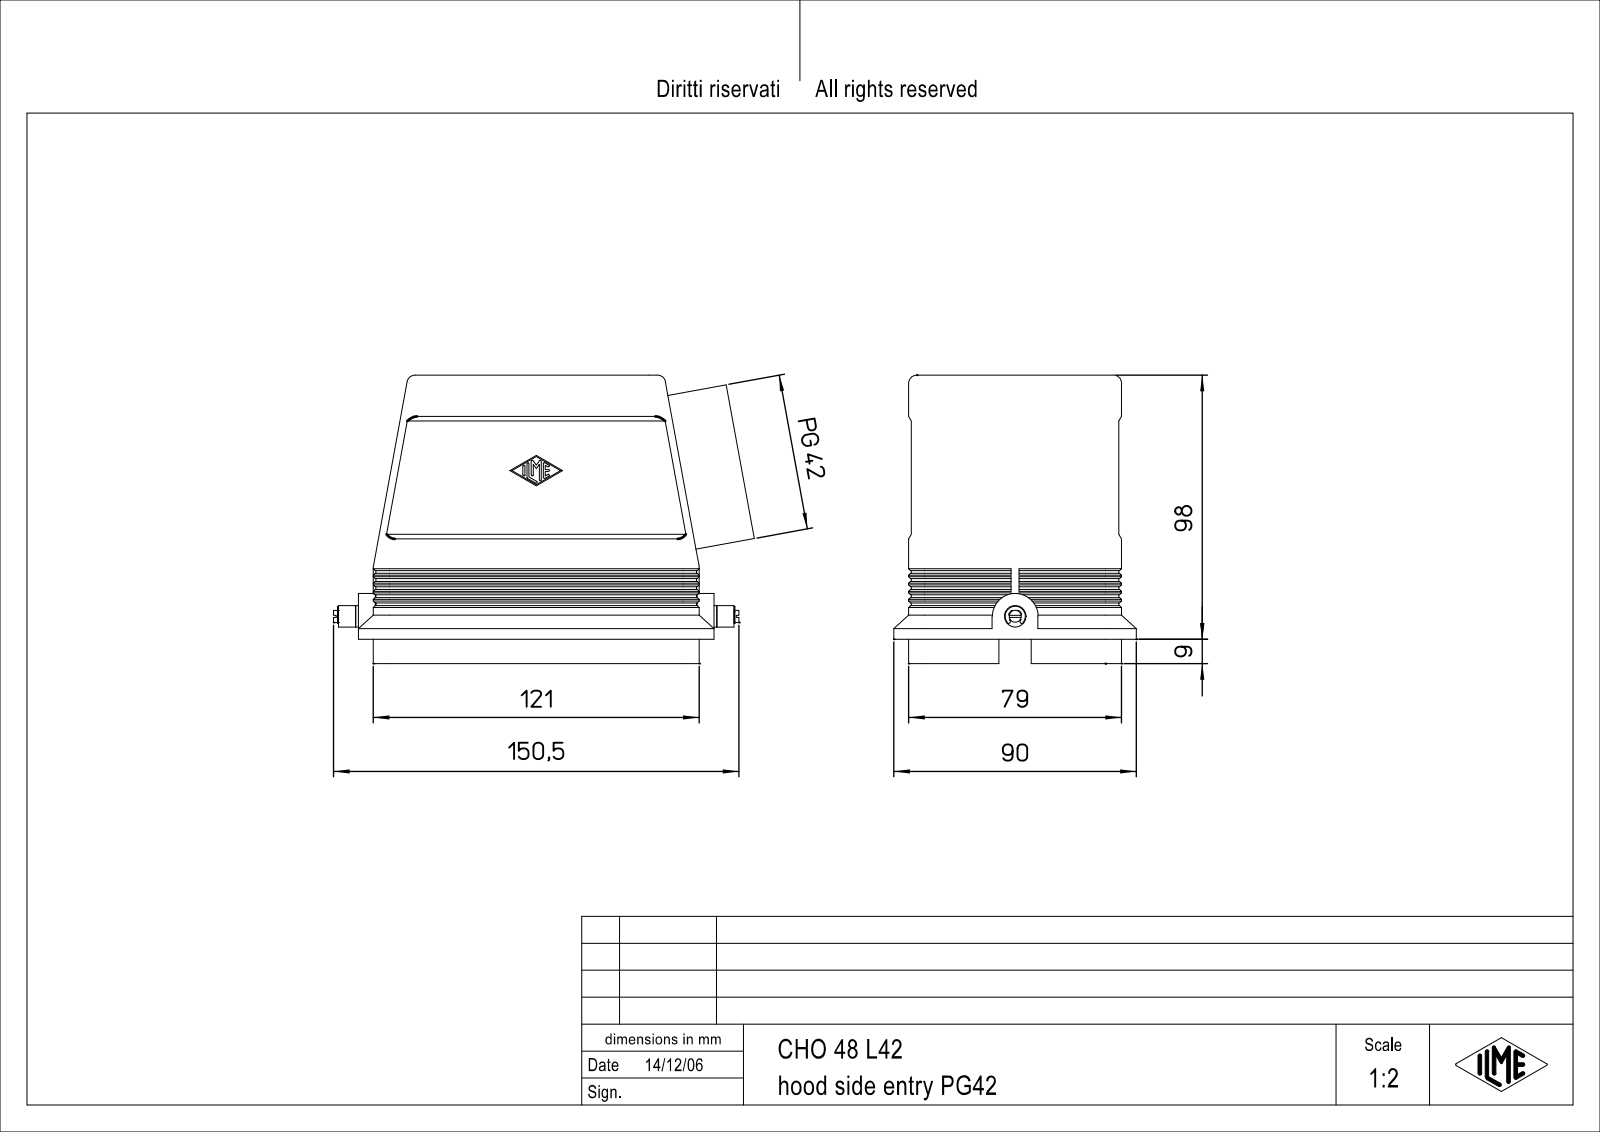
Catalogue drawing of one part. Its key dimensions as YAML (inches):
part_name: "CH_MH Tüllengehäuse Verschluss für 1 Bügel 104_62 Teil 1"
step_written_by: "Autodesk Inventor 7 (AUTOMOTIVE_DESIGN)"
units: inches
bodies: {solids: 1, faces: 683, planar: 241, cylindrical: 187, other: 255}
overall_size: [5.925, 4.213, 3.543]
volume: 14.86
surface_area: 157
round_holes:
  - {diameter: 0.097, count: 4}
  - {diameter: 0.138, count: 4}
  - {diameter: 0.236, count: 1}
  - {diameter: 1.318, count: 1}
  - {diameter: 1.397, count: 1}
  - {diameter: 1.89, count: 1}
round_bosses_or_shafts:
  - {diameter: 1.811, count: 1}
  - {diameter: 1.693, count: 1}
  - {diameter: 1.575, count: 1}
  - {diameter: 0.315, count: 1}
  - {diameter: 0.177, count: 1}
  - {diameter: 0.138, count: 1}
partial_cylinders:
  - {radius: 0.015, count: 14}
  - {radius: 0.079, count: 12}
  - {radius: 0.236, count: 10}
  - {radius: 0.02, count: 4}
  - {radius: 0.118, count: 4}
  - {radius: 0.453, count: 4}
  - {radius: 0.037, count: 3}
  - {radius: 0.024, count: 2}
face_to_face_distances: [2.835, 0.138, 2.972, 0.512, 0.098, 2.933, 0.039, 3.071, 3.11, 0.335]
hole_center_spacings: [1.063, 4.094, 4.23]
